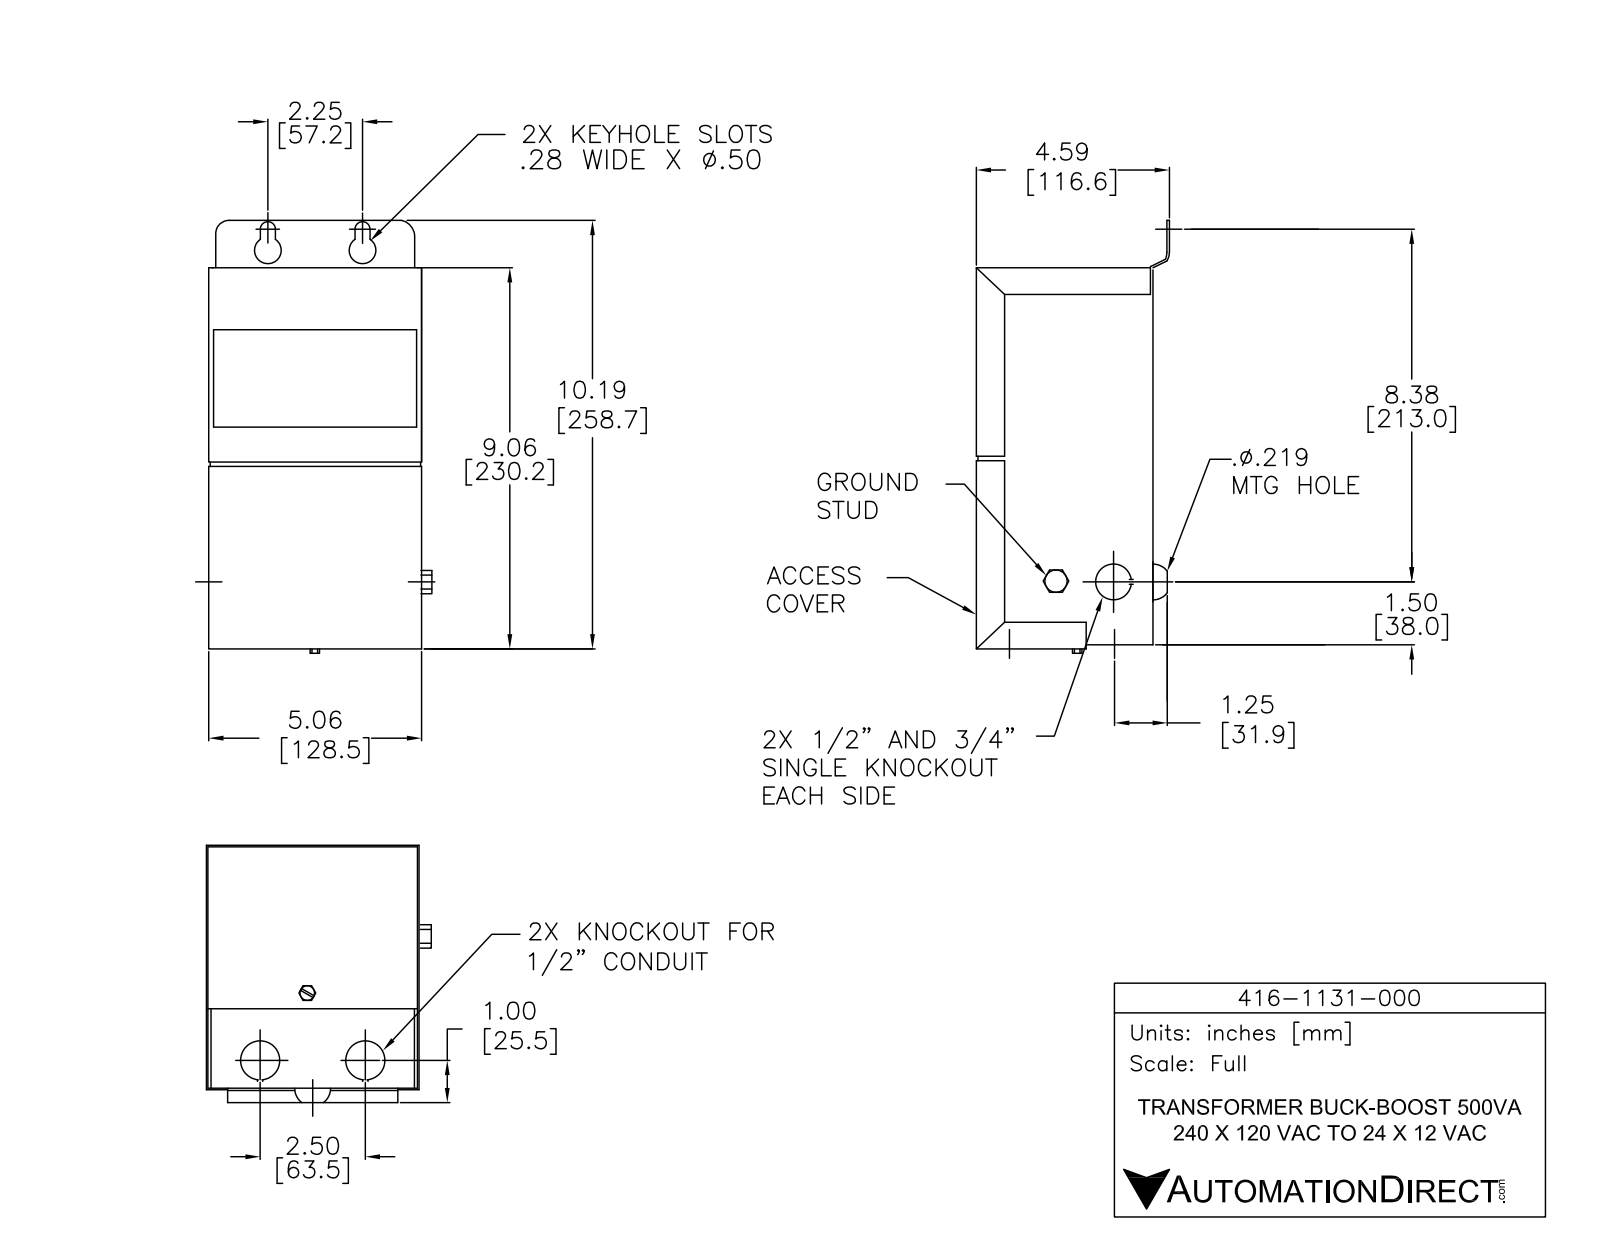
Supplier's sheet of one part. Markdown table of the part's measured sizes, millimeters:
| quantity | value |
| --- | --- |
| part name | 416-1131-000 |
| STEP written by | SolidWorks 2013 (AUTOMOTIVE_DESIGN) |
| units | millimeters |
| bodies | 1 solid, 159 faces (91 planar, 52 cylindrical, 16 other) |
| overall size | 261.6 × 131.3 × 116.6 |
| volume | 3 118 000 mm³ |
| surface area | 145 400 mm² |
| round holes (diameter × count) | 12.7 × 2, 22.2 × 2, 5.6 × 1, 5.9 × 1, 7.4 × 1, 22.2 × 1 |
| round bosses / shafts (diameter × count) | 28.6 × 1 |
| partial cylindrical surfaces (radius × count) | 1 × 10, 6.4 × 10, 3.6 × 2, 1.5 × 1, 3.8 × 1, 4.8 × 1 |
| main face-to-face distances | 106.7, 126.5, 1, 127.5, 106.7, 230.1, 128.5, 229.1, 1, 9.9 |
| hole center spacings | 43.7, 207.5, 34.8, 57.2, 63.5 |
